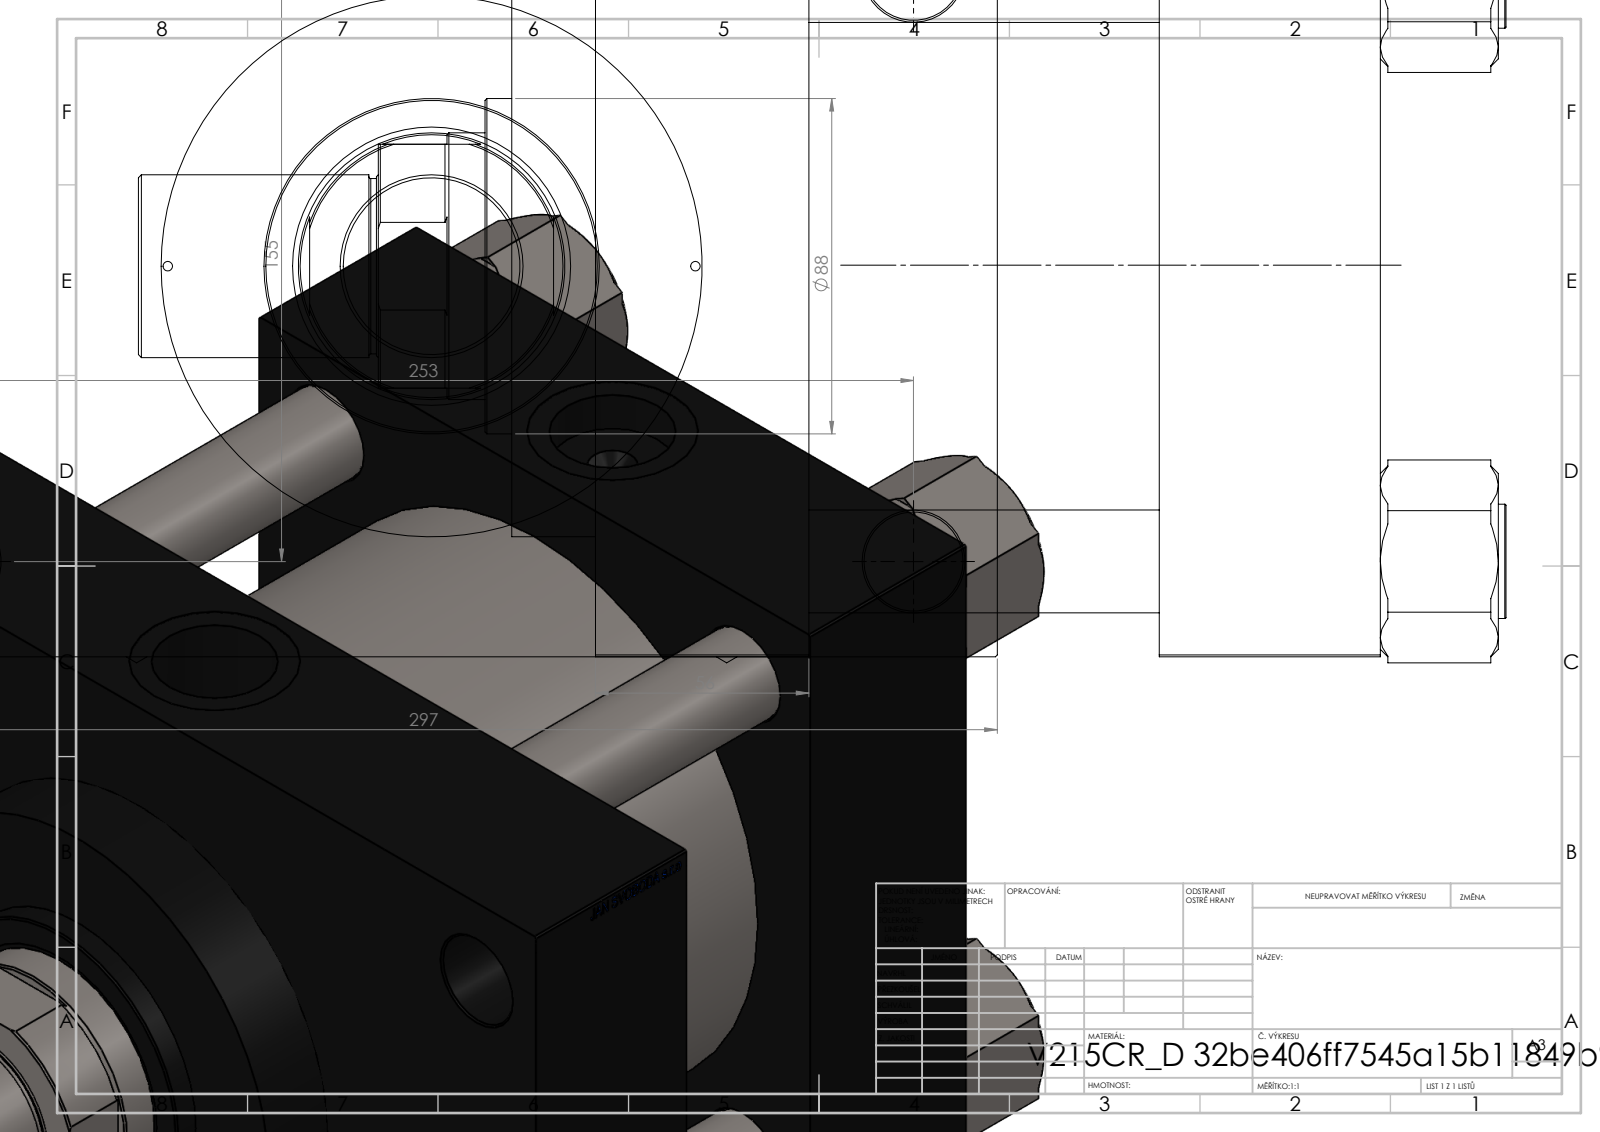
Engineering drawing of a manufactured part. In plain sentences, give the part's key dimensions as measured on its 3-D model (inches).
The part is named "V215CR_VCP_D; NUT_M5_D; V215CR_D_TYCINKA; V215_VC_A (+2 more)". Its 3-D file was written by "SolidWorks 2019 (CONFIG_CONTROL_DESIGN)". It is 12 solids with 1169 faces: 550 planar, 95 cylindrical and 524 other. Overall it measures 14.134 by 11.693 by 8.194 inches. Its volume is 488.7 cubic inches and its surface area 1 144 square inches. Round holes: 4 of diameter 1.024, 4 of diameter 1.063, 2 of diameter 0.098, 2 of diameter 0.276, 2 of diameter 1.309, 2 of diameter 1.772, 1 of diameter 1.831, 1 of diameter 2.756, 1 of diameter 2.874, 1 of diameter 4.724, 1 of diameter 5.591, 1 of diameter 6.299. Round bosses or shafts: 4 of diameter 1.181, 1 of diameter 6.535, 1 of diameter 3.465, 1 of diameter 1.89, 1 of diameter 1.811. Partial cylindrical surfaces (rounded edges, fillets, slot ends): 1 of radius 1.339. The main face-to-face distances are 2.283, 5.906, 3.622, 8.11, 5.827, 2.205, 8.071, 1.811, 9.882, 2.835. The hole center spacings are 1.931, 3.066, 3.793, 4.312, 5.841, 6.098, 6.399, 6.531.
